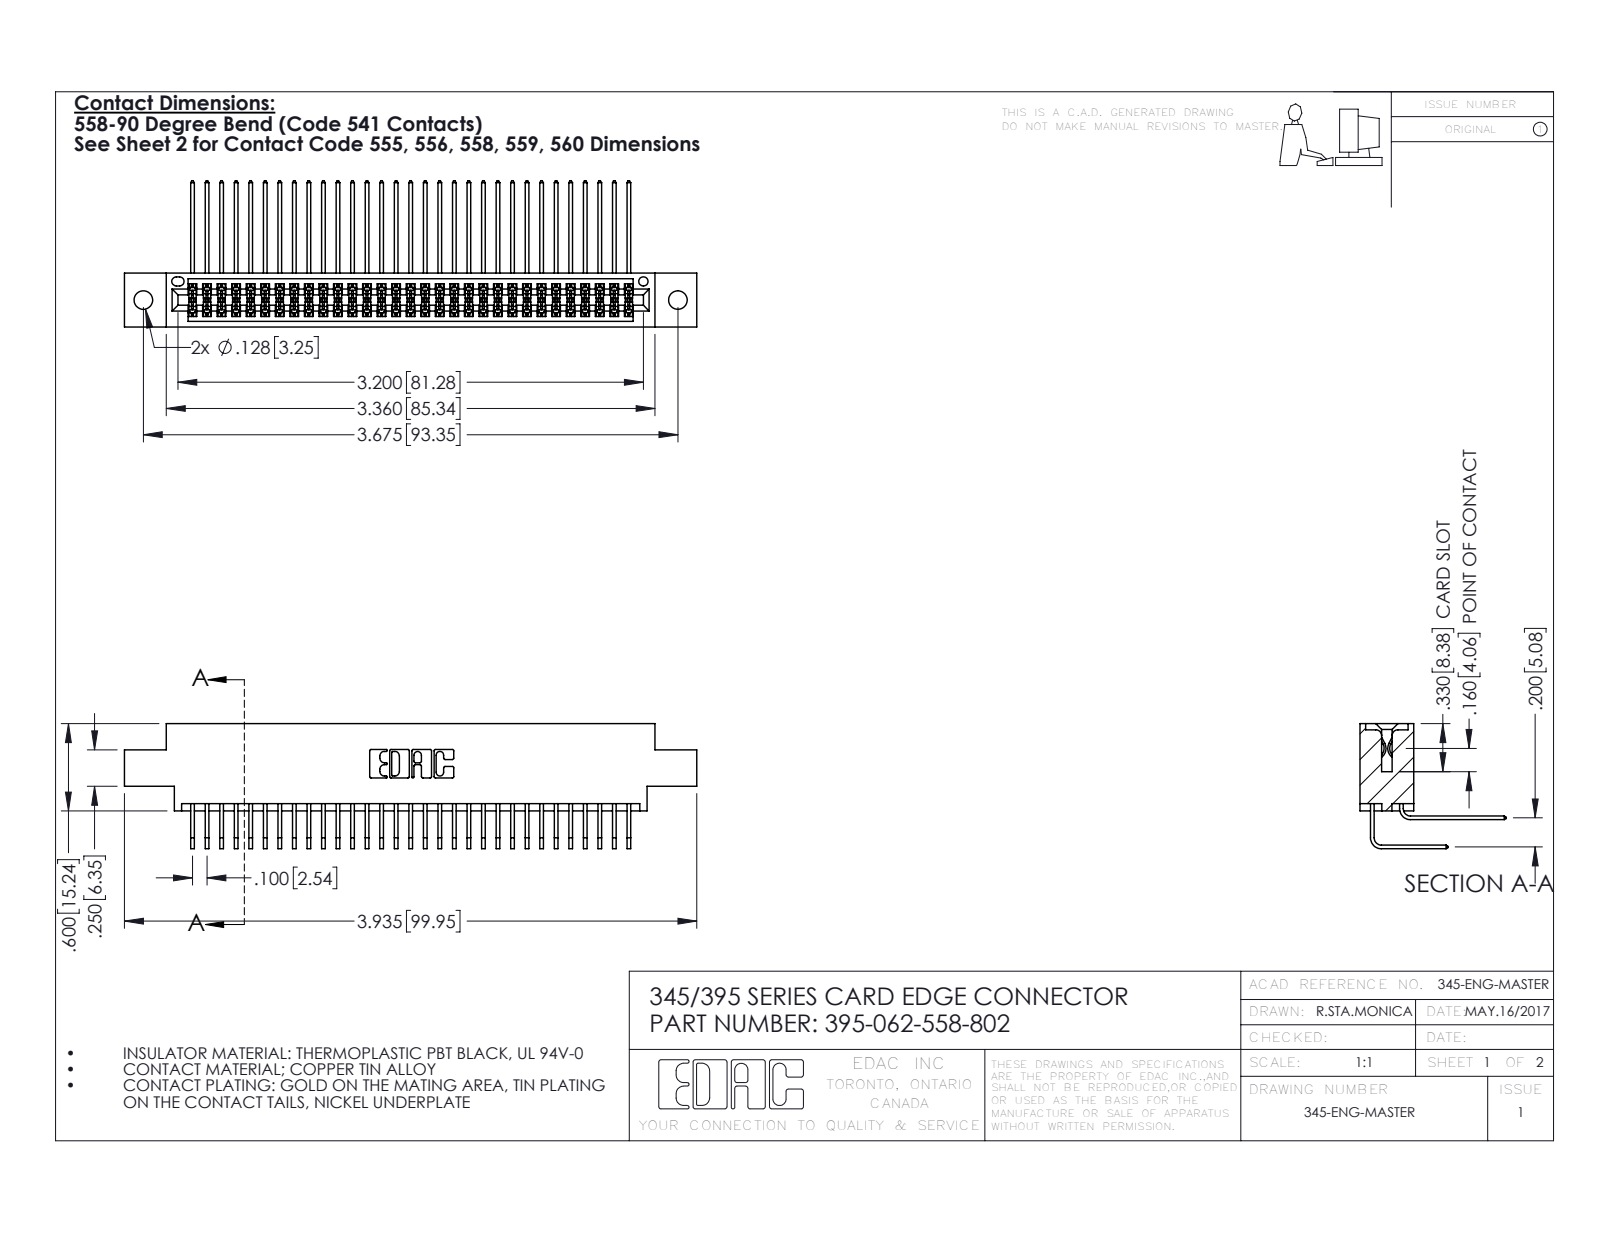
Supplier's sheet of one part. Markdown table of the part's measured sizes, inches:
| quantity | value |
| --- | --- |
| part name | 395-062-558-802; 345-292-001_558 Tail - 2; 345-292-001_558 559 Tail - 1; 345 Part_0.170 Offset - 0.128 Dia |
| STEP written by | SolidWorks 2016 (CONFIG_CONTROL_DESIGN) |
| units | inches |
| bodies | 63 solids, 3354 faces (2254 planar, 1100 cylindrical, 0 other) |
| overall size | 3.935 × 1.005 × 0.859 |
| volume | 0.599 in³ |
| surface area | 24.56 in² |
| round holes (diameter × count) | 0.128 × 2, 0.064 × 1 |
| partial cylindrical surfaces (radius × count) | 0.006 × 94, 0.01 × 22, 0.007 × 6, 0.031 × 6, 0.026 × 3, 0.014 × 2, 0.019 × 2, 0.022 × 2 |
| main face-to-face distances | 0.072, 0.298, 0.2, 0.37, 0.098, 0.272, 0.025, 0.225, 0.175, 0.025 |
| hole center spacings | 0.27, 3.44, 3.675 |
